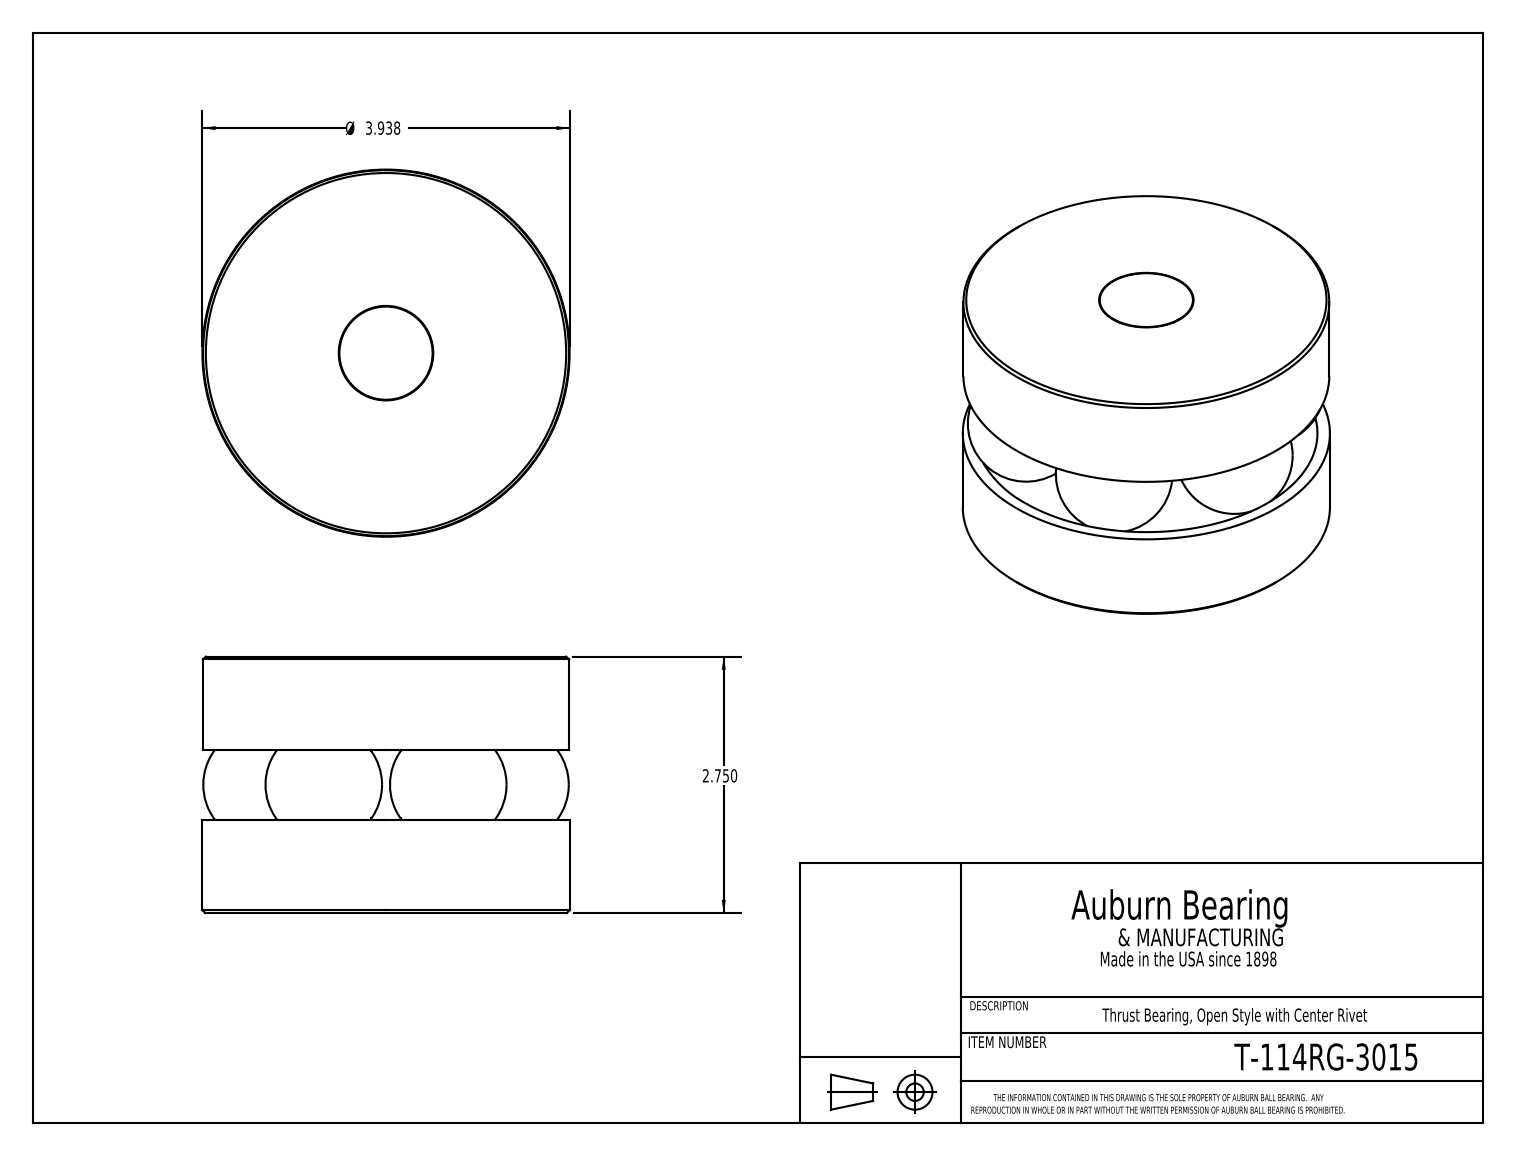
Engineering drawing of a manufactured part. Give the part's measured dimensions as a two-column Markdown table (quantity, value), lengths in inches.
| quantity | value |
| --- | --- |
| part name | T-114RG_T-114RG-3015 |
| STEP written by | SolidWorks 2016 (CONFIG_CONTROL_DESIGN) |
| units | inches |
| bodies | 9 solids, 27 faces (8 planar, 5 cylindrical, 14 other) |
| overall size | 3.938 × 3.938 × 2.75 |
| volume | 27.51 in³ |
| surface area | 112.1 in² |
| round holes (diameter × count) | 0.322 × 1 |
| round bosses / shafts (diameter × count) | 3.938 × 1, 3.924 × 1, 0.312 × 1 |
| main face-to-face distances | 2.75, 1, 1.75, 0.75 |
